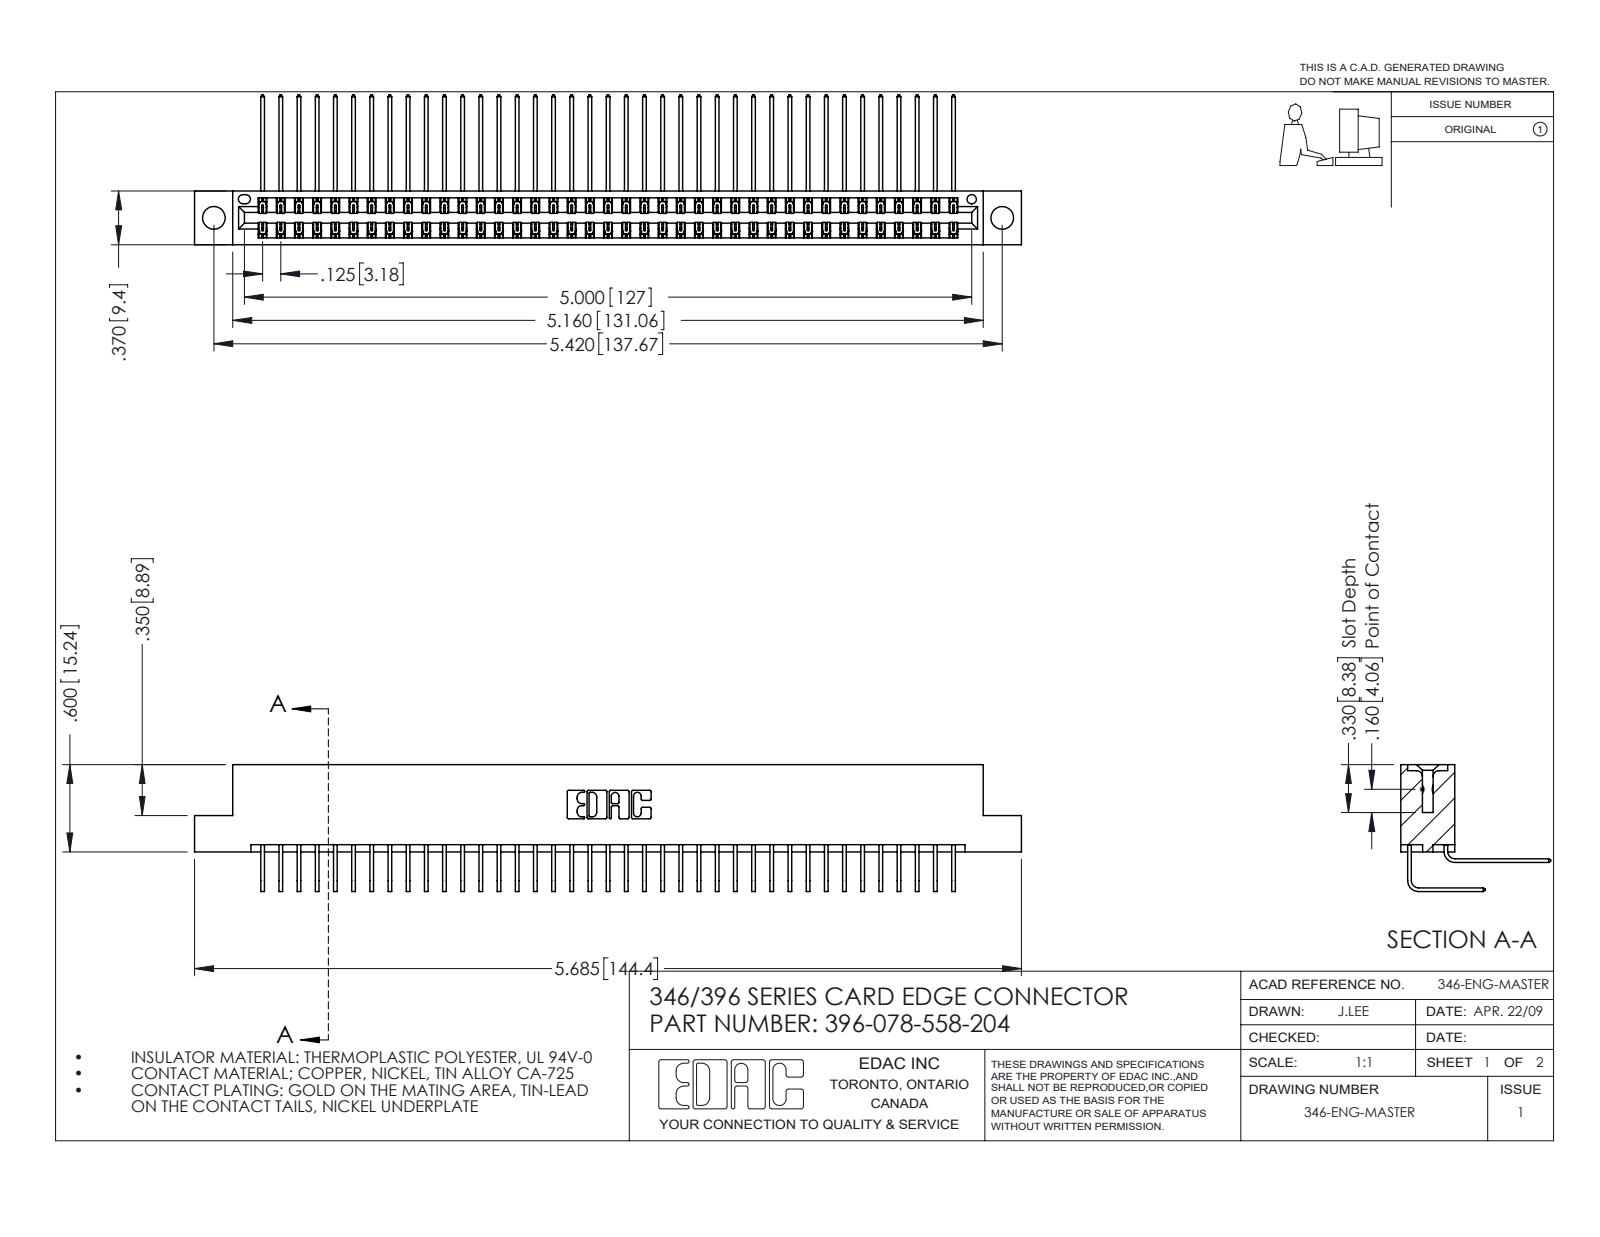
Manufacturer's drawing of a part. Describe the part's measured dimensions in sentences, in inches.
The part is named "345-292-001_558 559 Tail - 1; 396-078-558-204; 345-292-001_558 Tail - 2; 346 Part_Flush Mounting Lugs - 0.156 Dia-TH". Its 3-D file was written by "SolidWorks 2016 (CONFIG_CONTROL_DESIGN)". It is 79 solids with 4334 faces: 2962 planar, 1372 cylindrical and 0 other. Overall it measures 5.685 by 1.03 by 0.873 inches. Its volume is 0.88 cubic inches and its surface area 33.71 square inches. Round holes: 2 of diameter 0.156, 1 of diameter 0.064. Partial cylindrical surfaces (rounded edges, fillets, slot ends): 117 of radius 0.006, 22 of radius 0.01, 6 of radius 0.007, 6 of radius 0.031, 3 of radius 0.026, 2 of radius 0.014, 2 of radius 0.022, 2 of radius 0.024. The main face-to-face distances are 0.048, 0.322, 0.025, 0.37, 0.25, 0.072, 0.298, 0.275, 0.148, 0.222. The hole center spacings are 0.246, 5.211, 5.42.
